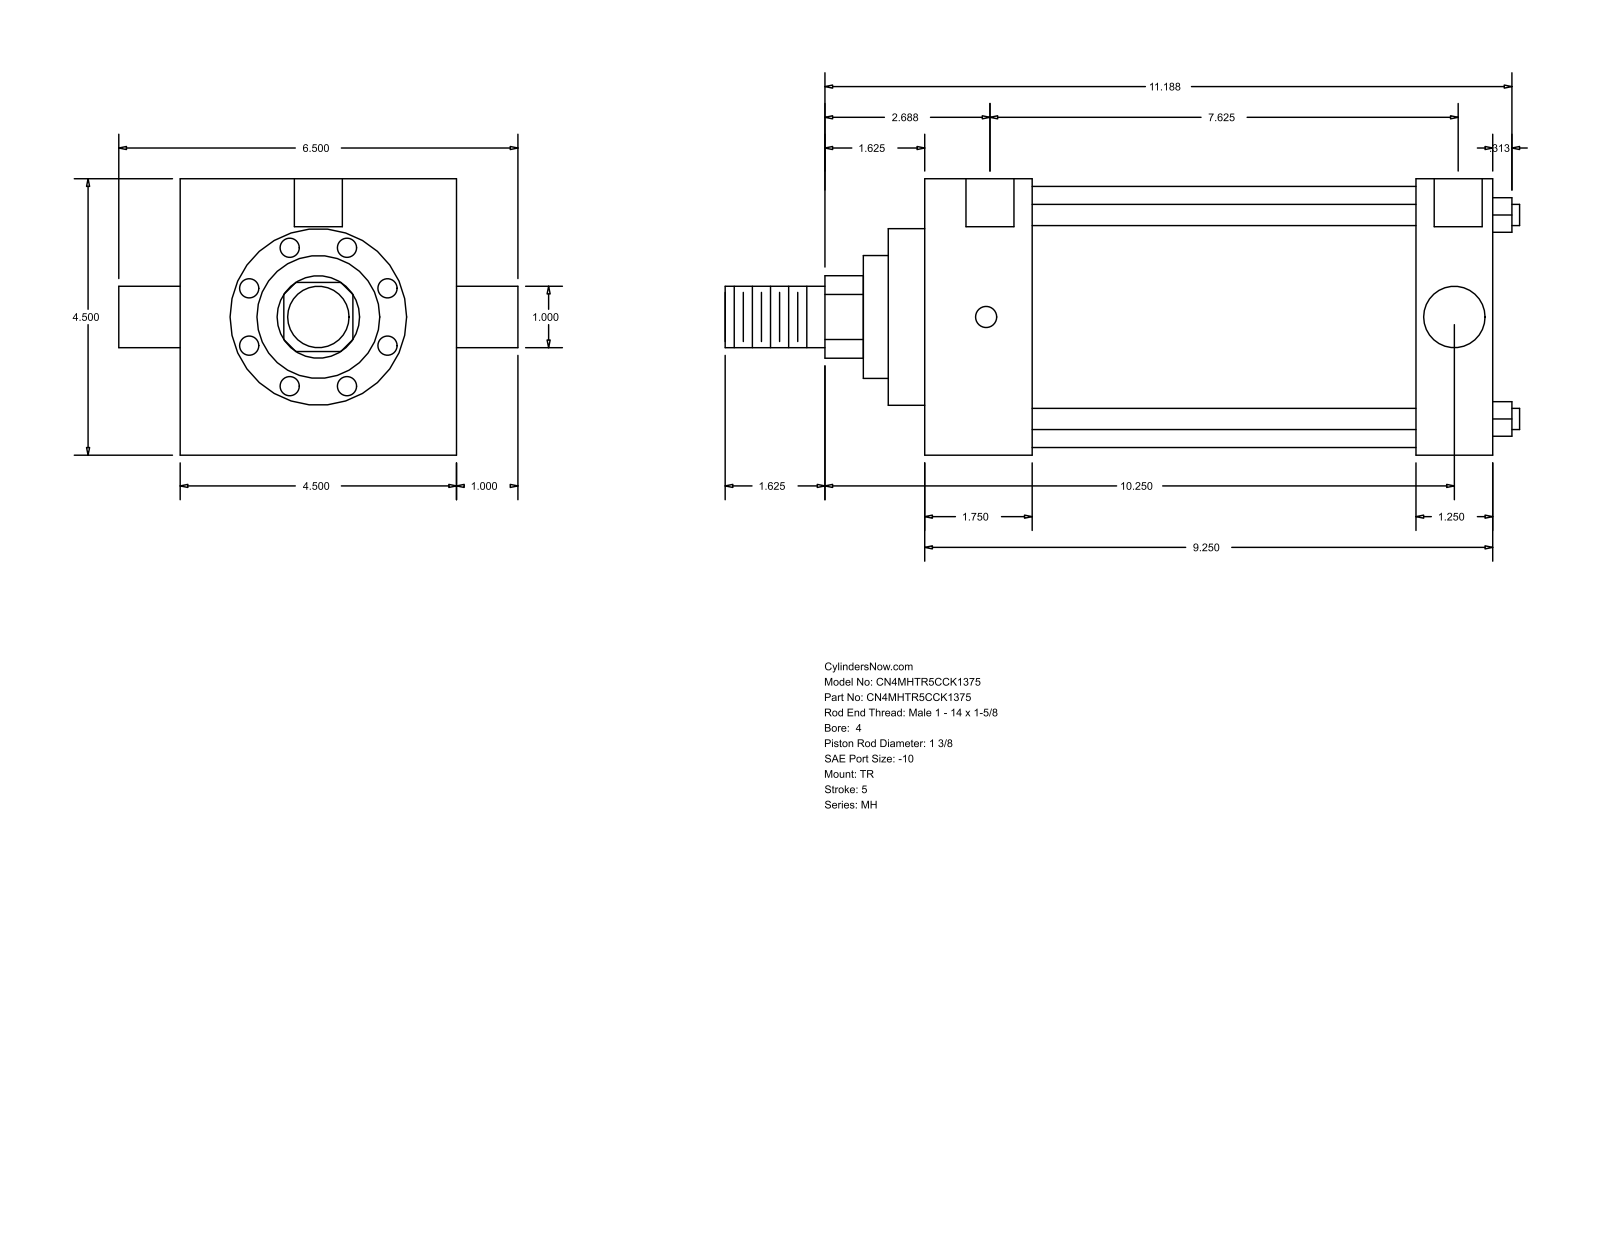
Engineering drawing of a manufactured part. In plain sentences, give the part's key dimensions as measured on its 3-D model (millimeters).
The part is named "MH_TR__0400_1.375". Its 3-D file was written by "GSSL Pune (CONFIG_CONTROL_DESIGN)". It is 0 solids with 86 faces: 61 planar, 25 cylindrical and 0 other. Overall it measures 328.61 by 165.1 by 114.3 millimeters. Round holes: 3 of diameter 8.73, 2 of diameter 19.84. Round bosses or shafts: 4 of diameter 8.76, 2 of diameter 25.4, 1 of diameter 107.95, 1 of diameter 73.03, 1 of diameter 50.8, 1 of diameter 34.92. Partial cylindrical surfaces (rounded edges, fillets, slot ends): 1 of radius 17.06. The main face-to-face distances are 114.3, 234.96, 44.45, 190.51, 203.2, 158.75, 31.76, 15.08, 59.53, 218.28. The hole center spacings are 1.58, 1.59, 193.68, 195.26, 195.27, 196.85.
